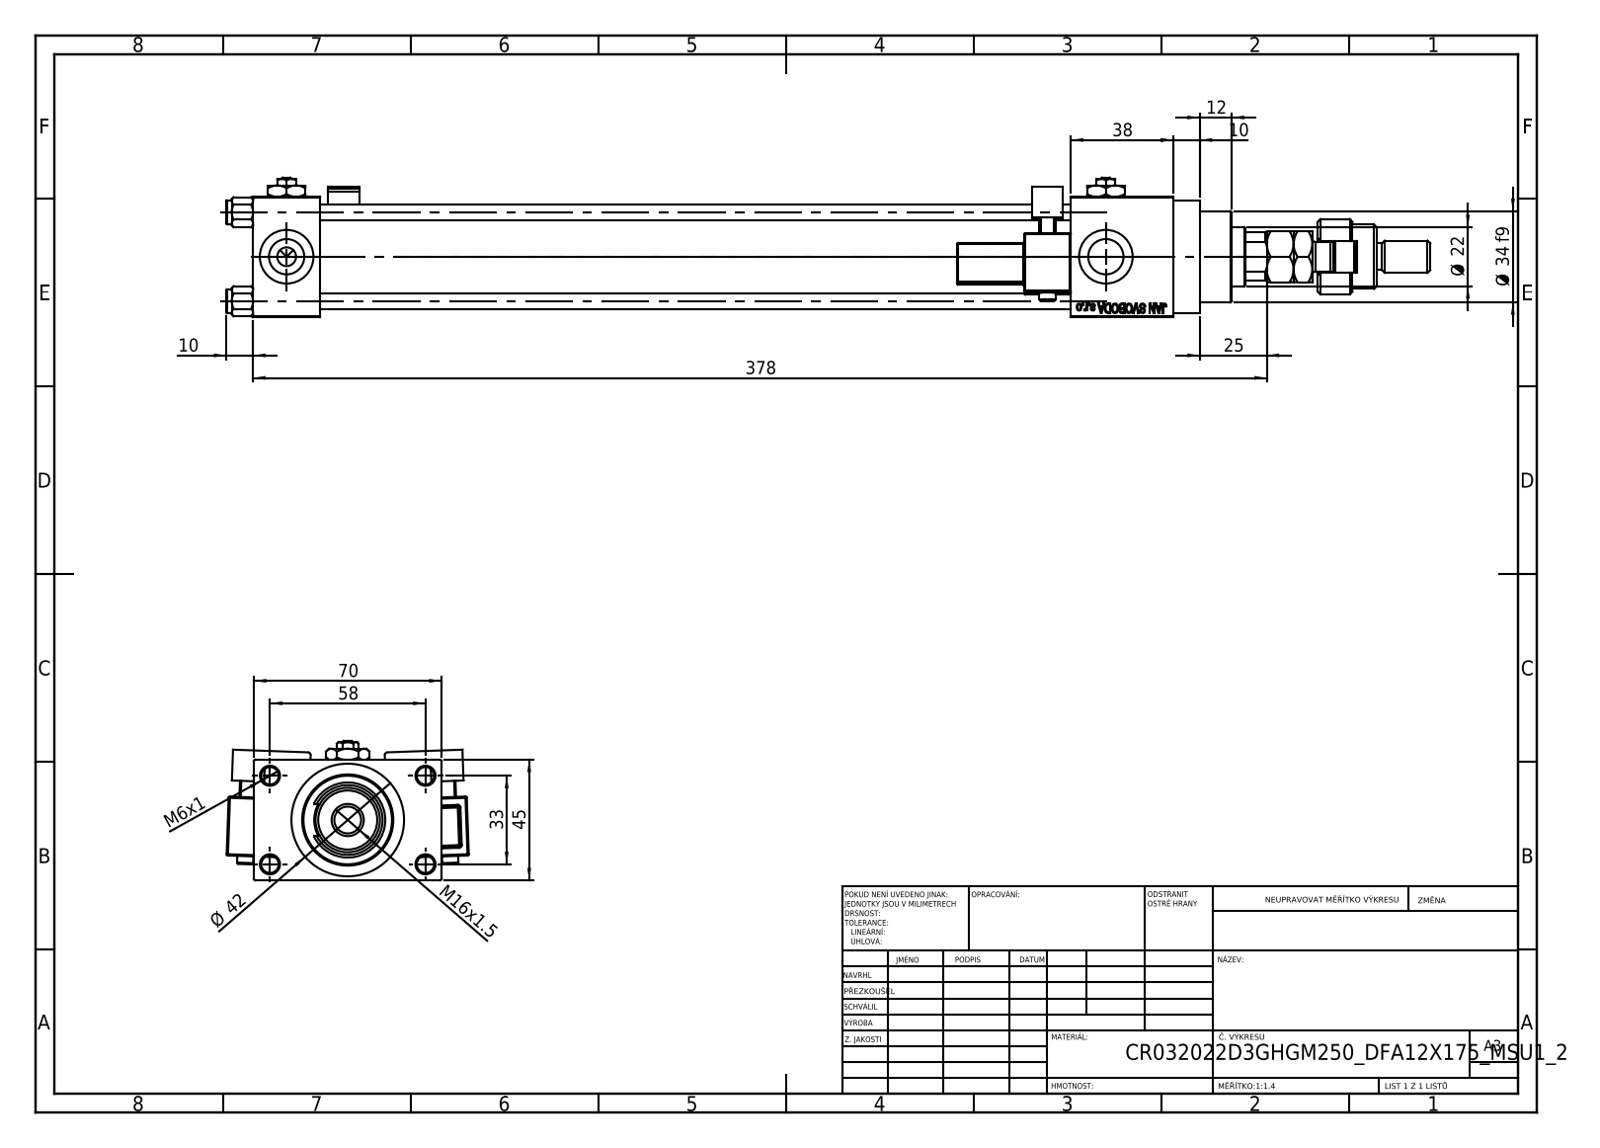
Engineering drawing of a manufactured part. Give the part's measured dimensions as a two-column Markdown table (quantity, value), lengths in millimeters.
| quantity | value |
| --- | --- |
| part name | MFA; V215CR_D_Body; V215_VC_A; V215CR_D_TYCINKA (+5 more) |
| STEP written by | SolidWorks 2019 (CONFIG_CONTROL_DESIGN) |
| units | millimeters |
| bodies | 17 solids, 1444 faces (632 planar, 172 cylindrical, 640 other) |
| overall size | 449 × 90.31 × 52 |
| volume | 489 595 mm³ |
| surface area | 184 652 mm² |
| round holes (diameter × count) | 6 × 4, 6.5 × 4, 13.16 × 4, 20 × 4, 7 × 3, 10.5 × 1, 22 × 1, 24 × 1, 25 × 1, 32 × 1, 33 × 1 |
| round bosses / shafts (diameter × count) | 9 × 4, 6 × 2, 42 × 1, 38 × 1, 34 × 1, 28 × 1, 18 × 1, 12 × 1 |
| partial cylindrical surfaces (radius × count) | 0.5 × 48, 1 × 2, 2.5 × 2, 4 × 2, 9.75 × 1, 10.5 × 1 |
| main face-to-face distances | 45, 25, 280, 12.5, 3, 305, 57.5, 318, 38, 343 |
| hole center spacings | 12.4, 23.48, 33.2, 33.37, 35.35, 45.6, 56.35, 33 |
